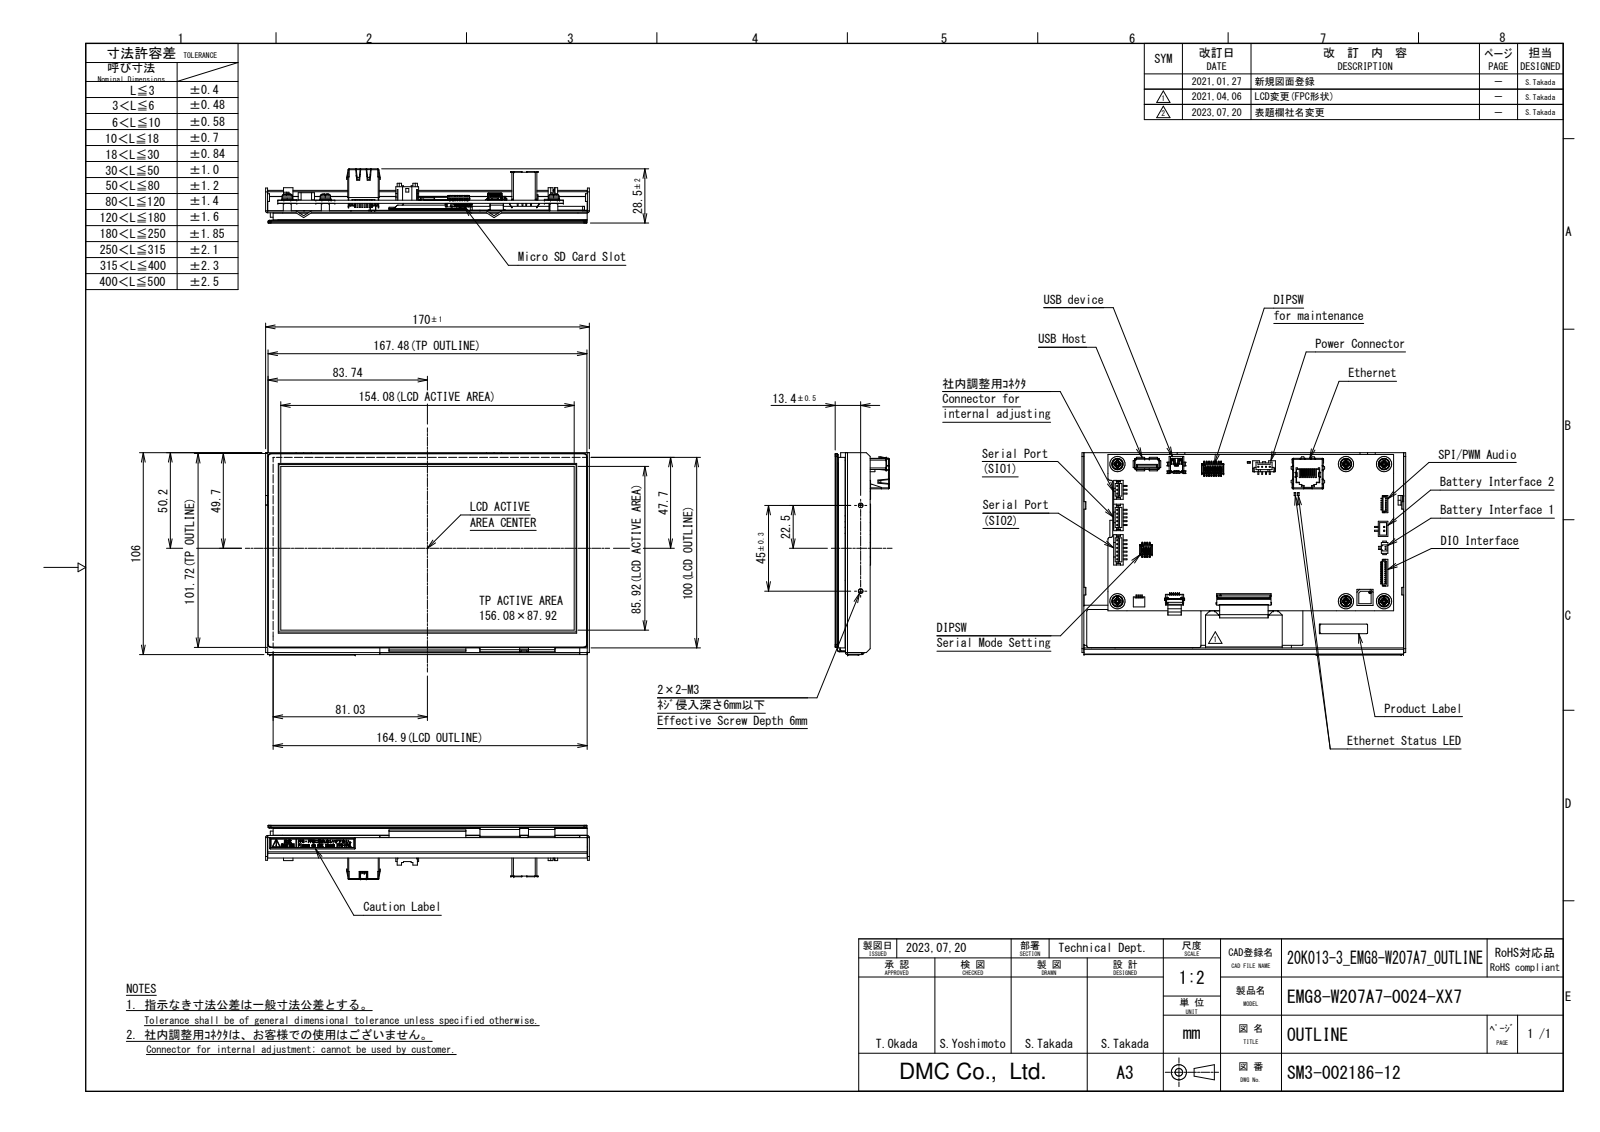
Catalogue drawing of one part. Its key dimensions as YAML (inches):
part_name: "HP_EMG8-W207A7-0024-XX7_parts"
step_written_by: "Autodesk Inventor 2020 (AUTOMOTIVE_DESIGN)"
units: inches
bodies: {solids: 1, faces: 6317, planar: 4771, cylindrical: 945, other: 601}
overall_size: [6.693, 4.181, 1.121]
volume: 8.329
surface_area: 215.2
round_holes:
  - {diameter: 0.097, count: 8}
  - {diameter: 0.138, count: 6}
  - {diameter: 0.315, count: 6}
  - {diameter: 0.047, count: 2}
  - {diameter: 0.012, count: 1}
  - {diameter: 0.052, count: 1}
round_bosses_or_shafts:
  - {diameter: 0.236, count: 6}
  - {diameter: 0.217, count: 6}
  - {diameter: 0.165, count: 6}
  - {diameter: 0.142, count: 6}
  - {diameter: 0.118, count: 6}
  - {diameter: 0.157, count: 2}
partial_cylinders:
  - {radius: 0.004, count: 208}
  - {radius: 0.006, count: 57}
  - {radius: 0.008, count: 48}
  - {radius: 0.02, count: 42}
  - {radius: 0.01, count: 29}
  - {radius: 0.012, count: 28}
  - {radius: 0.039, count: 17}
  - {radius: 0.005, count: 16}
face_to_face_distances: [0.146, 0.192, 0.251, 0.059, 0.185, 0.065, 0.039, 0.408, 0.157, 0.343]
hole_center_spacings: [2.835, 0.787, 2.942, 4.724, 5.509, 5.512, 6.198, 0.342]
